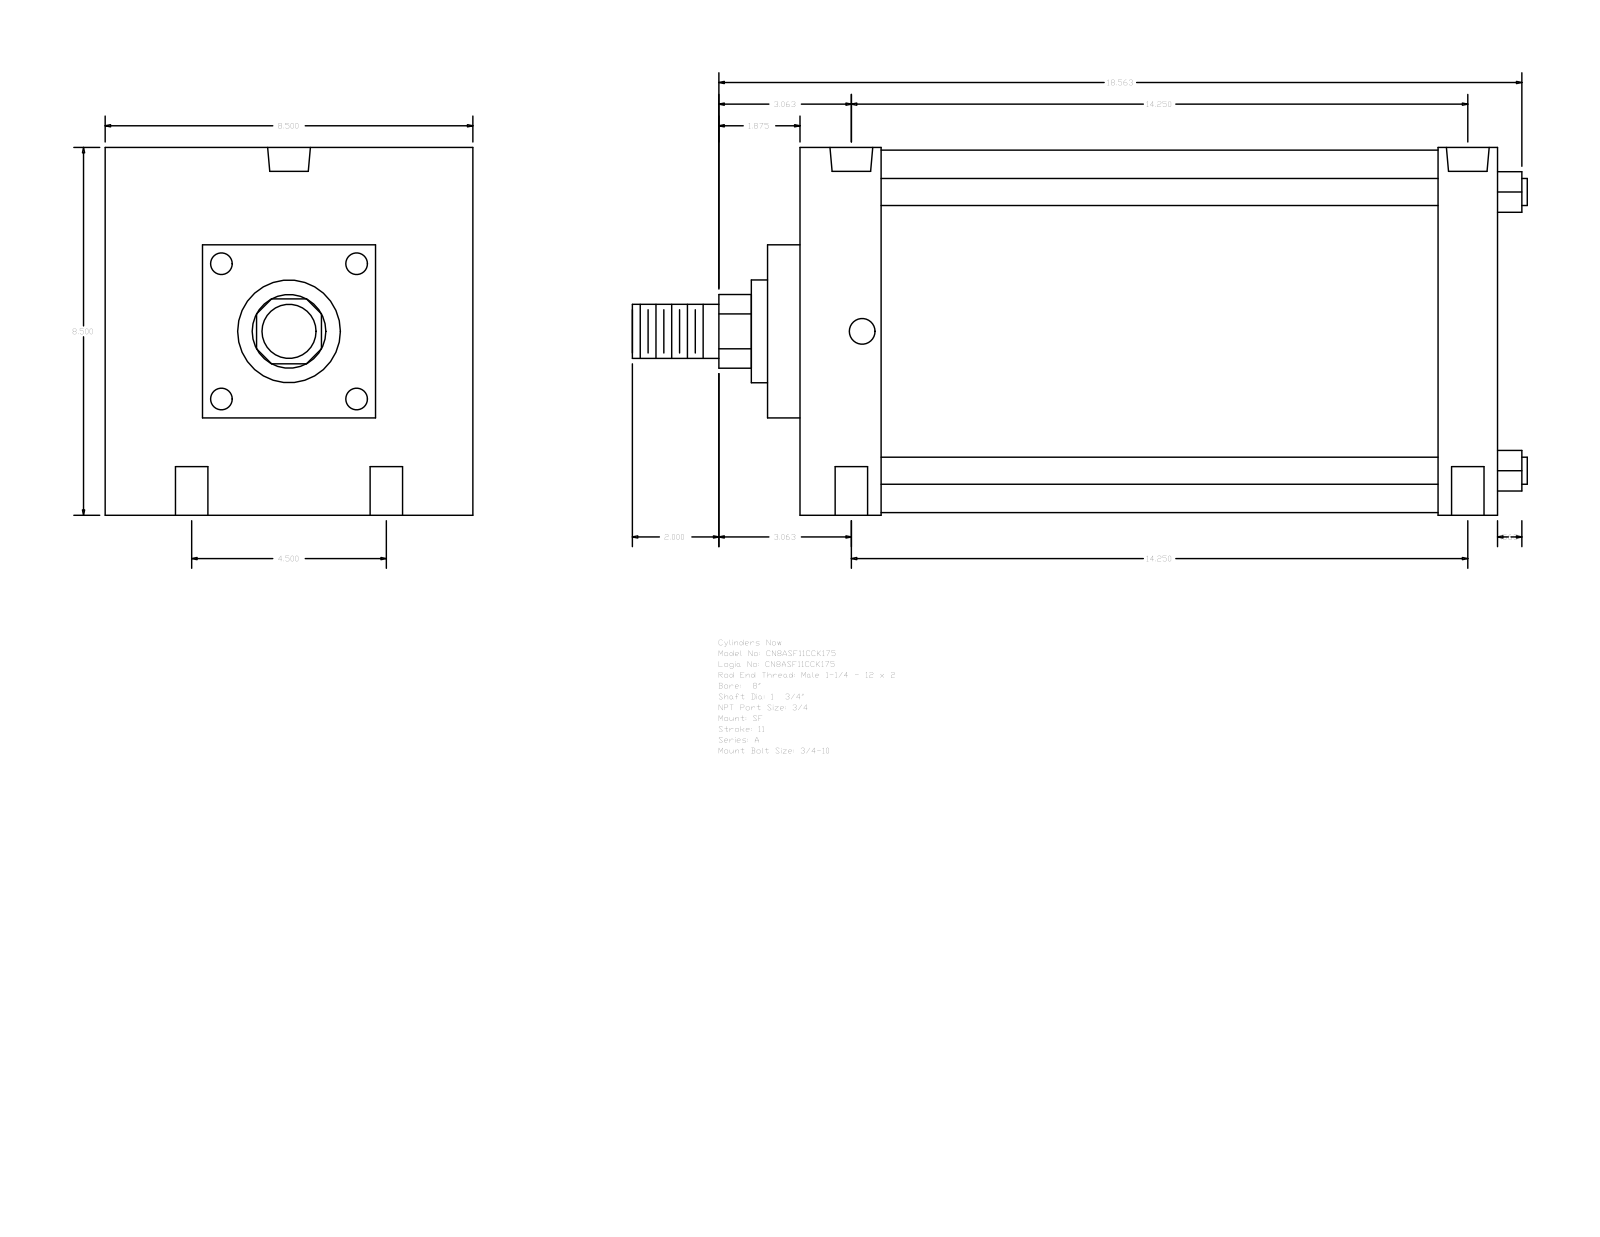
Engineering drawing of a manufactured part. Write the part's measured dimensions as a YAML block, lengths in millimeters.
part_name: "A_SF__0800_1.75"
step_written_by: "GSSL Pune (CONFIG_CONTROL_DESIGN)"
units: millimeters
bodies: {solids: 0, faces: 93, planar: 67, cylindrical: 26, other: 0}
overall_size: [525.46, 215.9, 215.9]
round_holes:
  - {diameter: 19.05, count: 4}
  - {diameter: 15.08, count: 2}
  - {diameter: 25.12, count: 2}
round_bosses_or_shafts:
  - {diameter: 15.88, count: 4}
  - {diameter: 212.72, count: 1}
  - {diameter: 60.33, count: 1}
  - {diameter: 44.45, count: 1}
  - {diameter: 31.75, count: 1}
partial_cylinders:
  - {radius: 21.63, count: 1}
face_to_face_distances: [409.58, 215.9, 47.63, 374.65, 327.02, 361.95, 34.93, 19.05, 158.75, 57.15]
hole_center_spacings: [57.15, 366.43, 361.95, 114.3, 379.57, 349.25]
